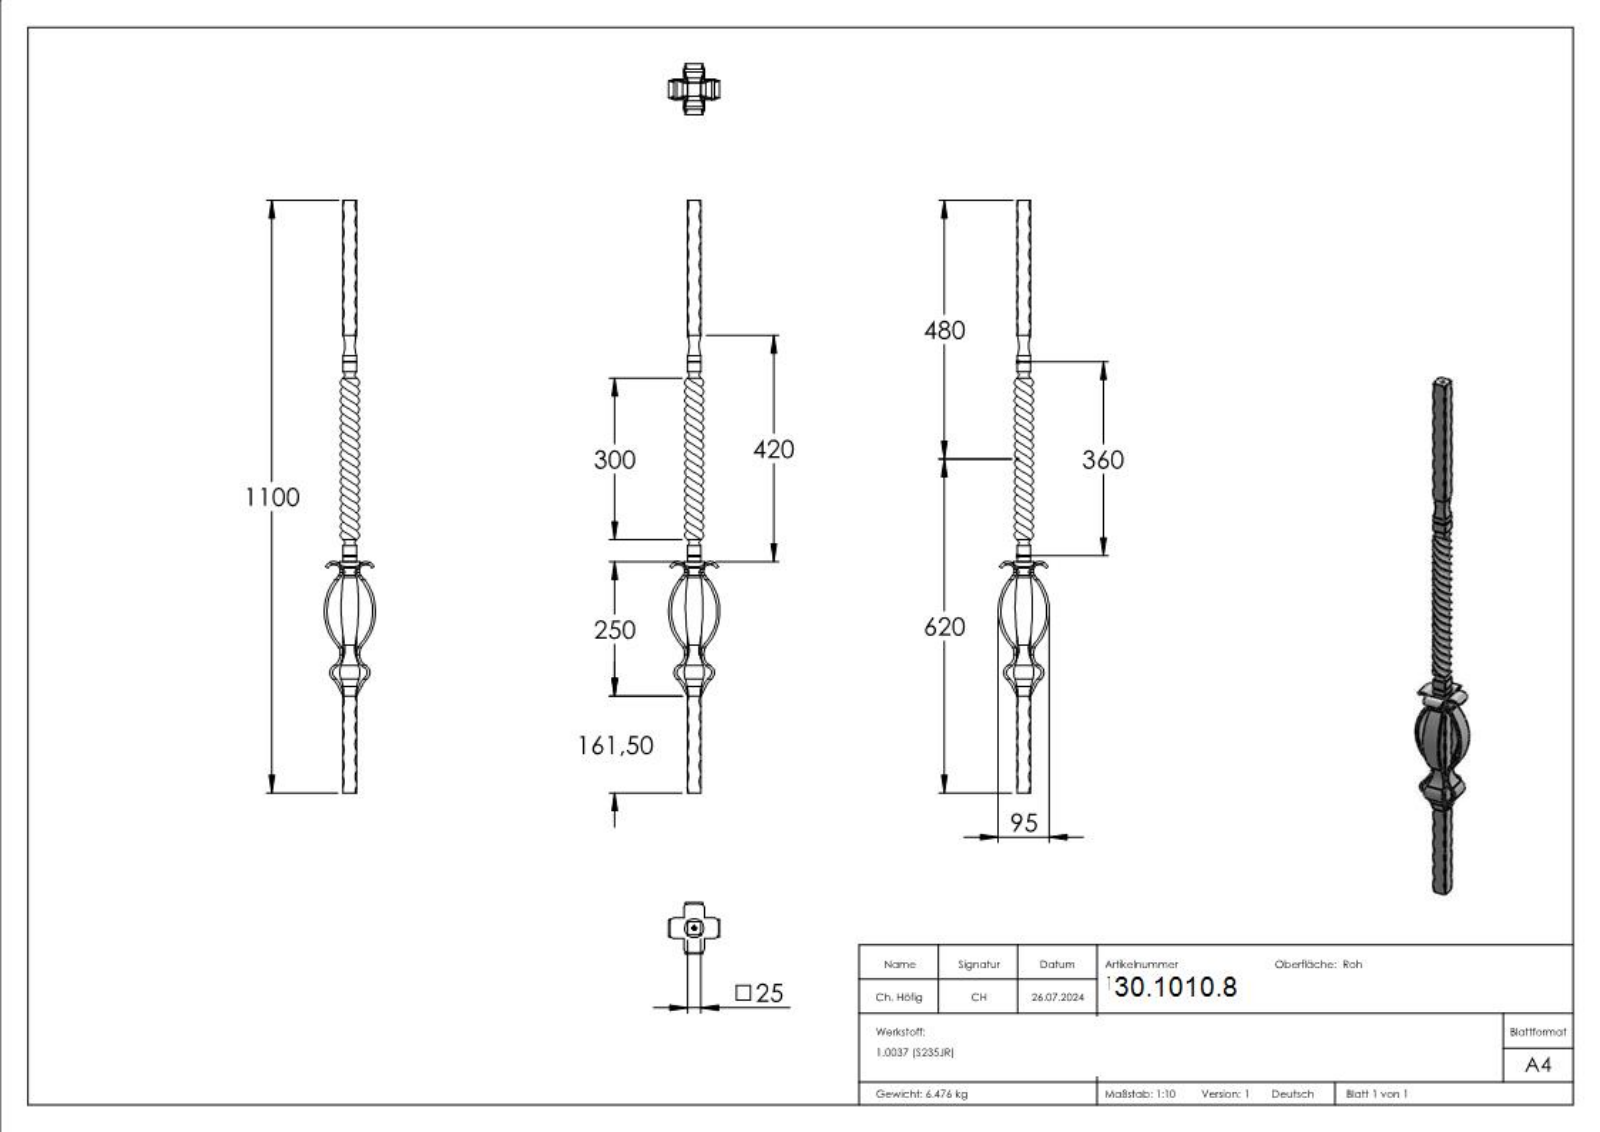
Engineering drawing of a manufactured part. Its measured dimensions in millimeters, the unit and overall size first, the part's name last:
Units: millimetres
Overall size (bounding box): 1100 × 95 × 95
Partial cylindrical surfaces — rounded edges, fillets, slot ends (radius × count): R10 ×16, R30 ×12, R5 ×4, R12.45 ×4, R15 ×4, R17.45 ×4, R25 ×4, R33.28 ×4
Main face-to-face distances: 25, 1100, 6.5, 31.5, 7.5, 30.5, 1, 24, 38, 2
Volume: 830 649 mm³ · Surface area: 196 693 mm²
Bodies: 5 solids, 494 faces (165 planar, 128 cylindrical, 201 other)
Part name (STEP PRODUCT): 1012
STEP written by: SolidWorks 2018 (CONFIG_CONTROL_DESIGN)
